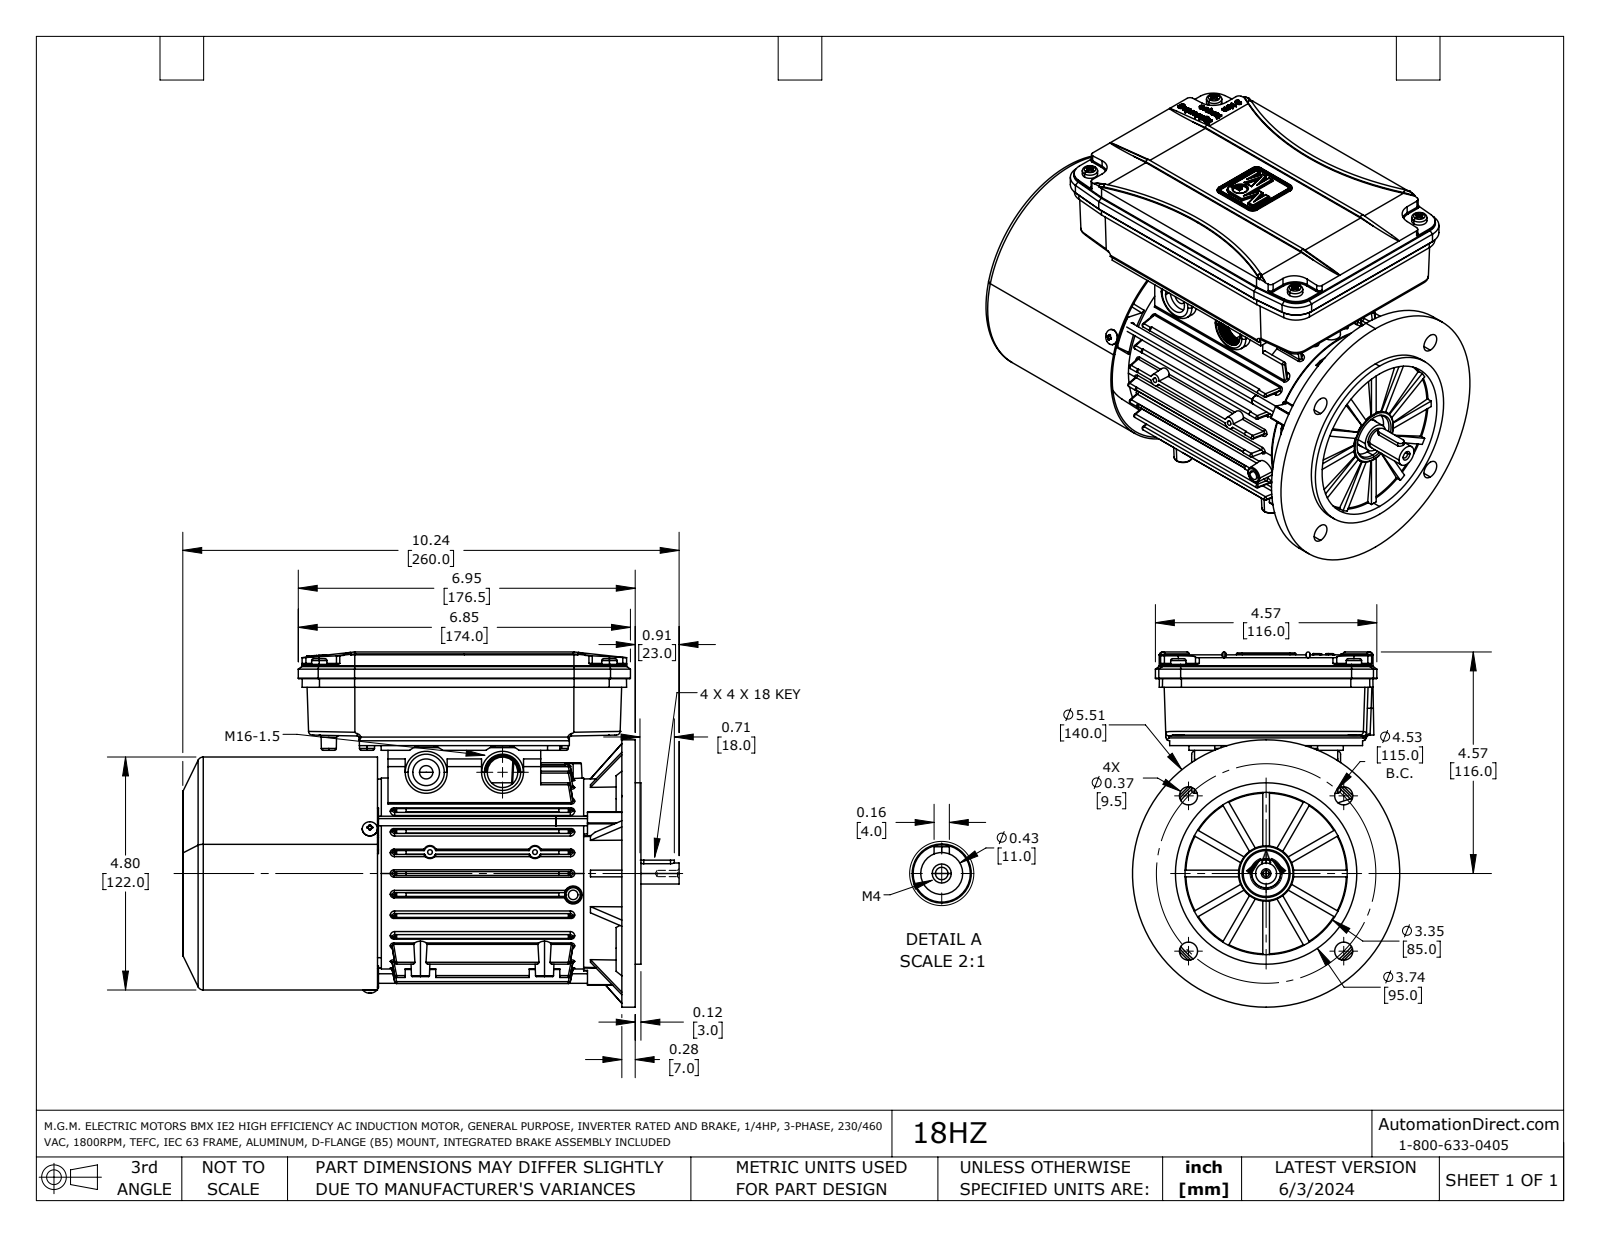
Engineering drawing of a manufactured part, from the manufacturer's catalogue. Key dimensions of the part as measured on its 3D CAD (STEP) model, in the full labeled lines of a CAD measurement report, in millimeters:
Part name (STEP PRODUCT): 18HZ
STEP written by: SolidWorks 2021 (AUTOMOTIVE_DESIGN)
Units: millimetres
Bodies: 28 solids, 4146 faces (1489 planar, 1278 cylindrical, 1379 other)
Overall size (bounding box): 260 × 186 × 140
Volume: 715 800 mm³ · Surface area: 467 900 mm²
Round holes (diameter × count): ⌀3.3 ×16, ⌀4.5 ×12, ⌀4 ×11, ⌀2.5 ×9, ⌀5.5 ×7, ⌀6 ×7, ⌀5 ×6, ⌀3 ×4, ⌀9.5 ×4, ⌀3.2 ×3, ⌀4.2 ×3, ⌀7 ×3
Round bosses / shafts (diameter × count): ⌀4.5 ×8, ⌀3 ×8, ⌀8 ×7, ⌀5 ×3, ⌀2 ×3, ⌀140 ×1, ⌀122 ×1, ⌀100 ×1
Partial cylindrical surfaces — rounded edges, fillets, slot ends (radius × count): R1 ×310, R0.5 ×56, R0.4 ×42, R0.2 ×32, R2 ×29, R0.3 ×24, R0.1 ×16, R2.2 ×16
Main face-to-face distances: 2, 11, 9, 2, 7, 30.9, 37.9, 39.9, 28.9, 9
Hole centre spacings: 94.4, 18.9, 19.9, 25.8, 29.5, 41.8, 42.7, 55
